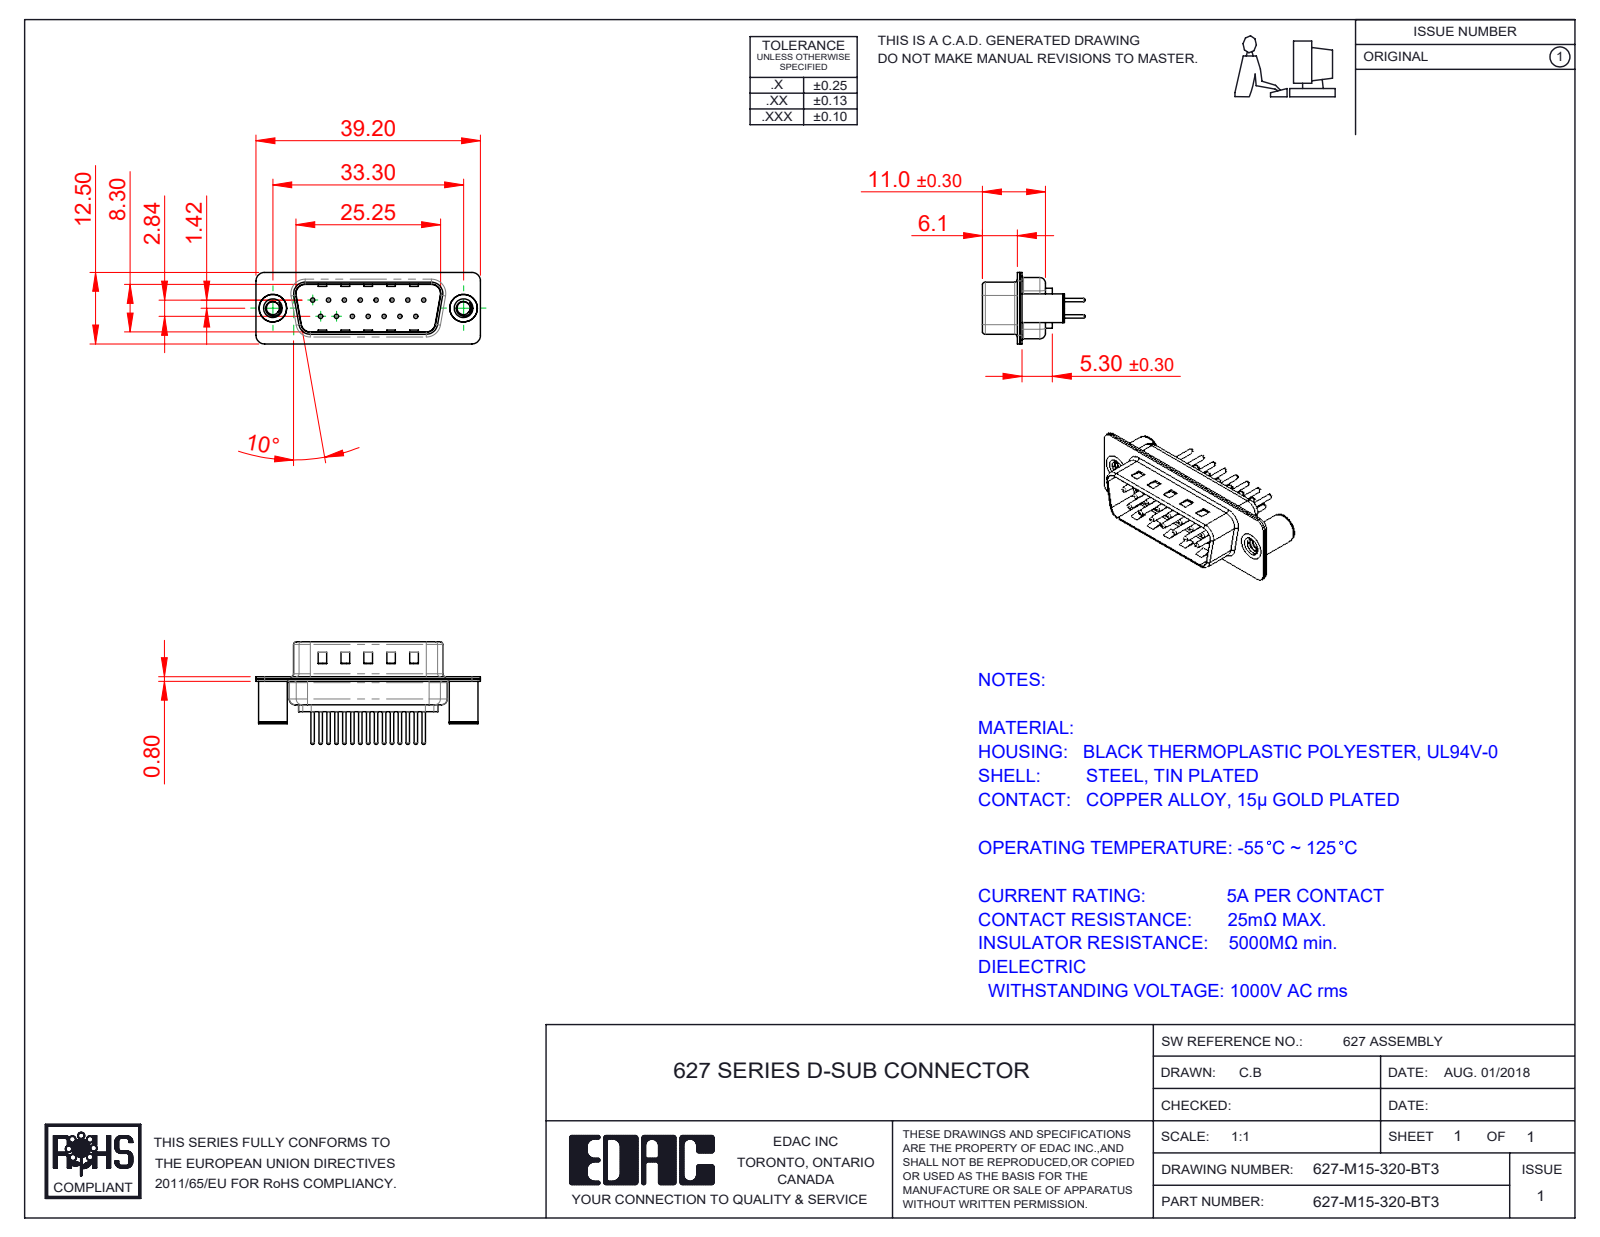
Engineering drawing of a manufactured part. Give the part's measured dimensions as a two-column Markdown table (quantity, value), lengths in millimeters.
| quantity | value |
| --- | --- |
| part name | 627M Shell Front_15 Contacts; 627M 4-40 Threaded Board Spacer; 627-M15-320-BT3; 627M Housing_15 Contacts (+3 more) |
| STEP written by | SolidWorks 2020 (CONFIG_CONTROL_DESIGN) |
| units | millimeters |
| bodies | 20 solids, 929 faces (244 planar, 367 cylindrical, 318 other) |
| overall size | 39.2 × 17.9 × 12.5 |
| volume | 1 966 mm³ |
| surface area | 5 067 mm² |
| round holes (diameter × count) | 0.75 × 15, 1.6 × 15, 2 × 15, 2.26 × 2, 3.26 × 2, 4 × 2, 4.8 × 2 |
| round bosses / shafts (diameter × count) | 1.5 × 15, 0.6 × 15, 5 × 2, 4.9 × 2 |
| partial cylindrical surfaces (radius × count) | 1.5 × 16, 2 × 12, 0.5 × 8, 1.6 × 8, 0.25 × 4, 0.6 × 4, 0.65 × 4, 0.9 × 4 |
| main face-to-face distances | 0.4, 0.8, 9.5, 9.1, 8.7, 9.9, 1.2, 5.3, 6.1, 5.7 |
| hole center spacings | 3.16, 2.77, 5.54, 8.31, 11.08, 5.03, 5.04, 7.48 |
